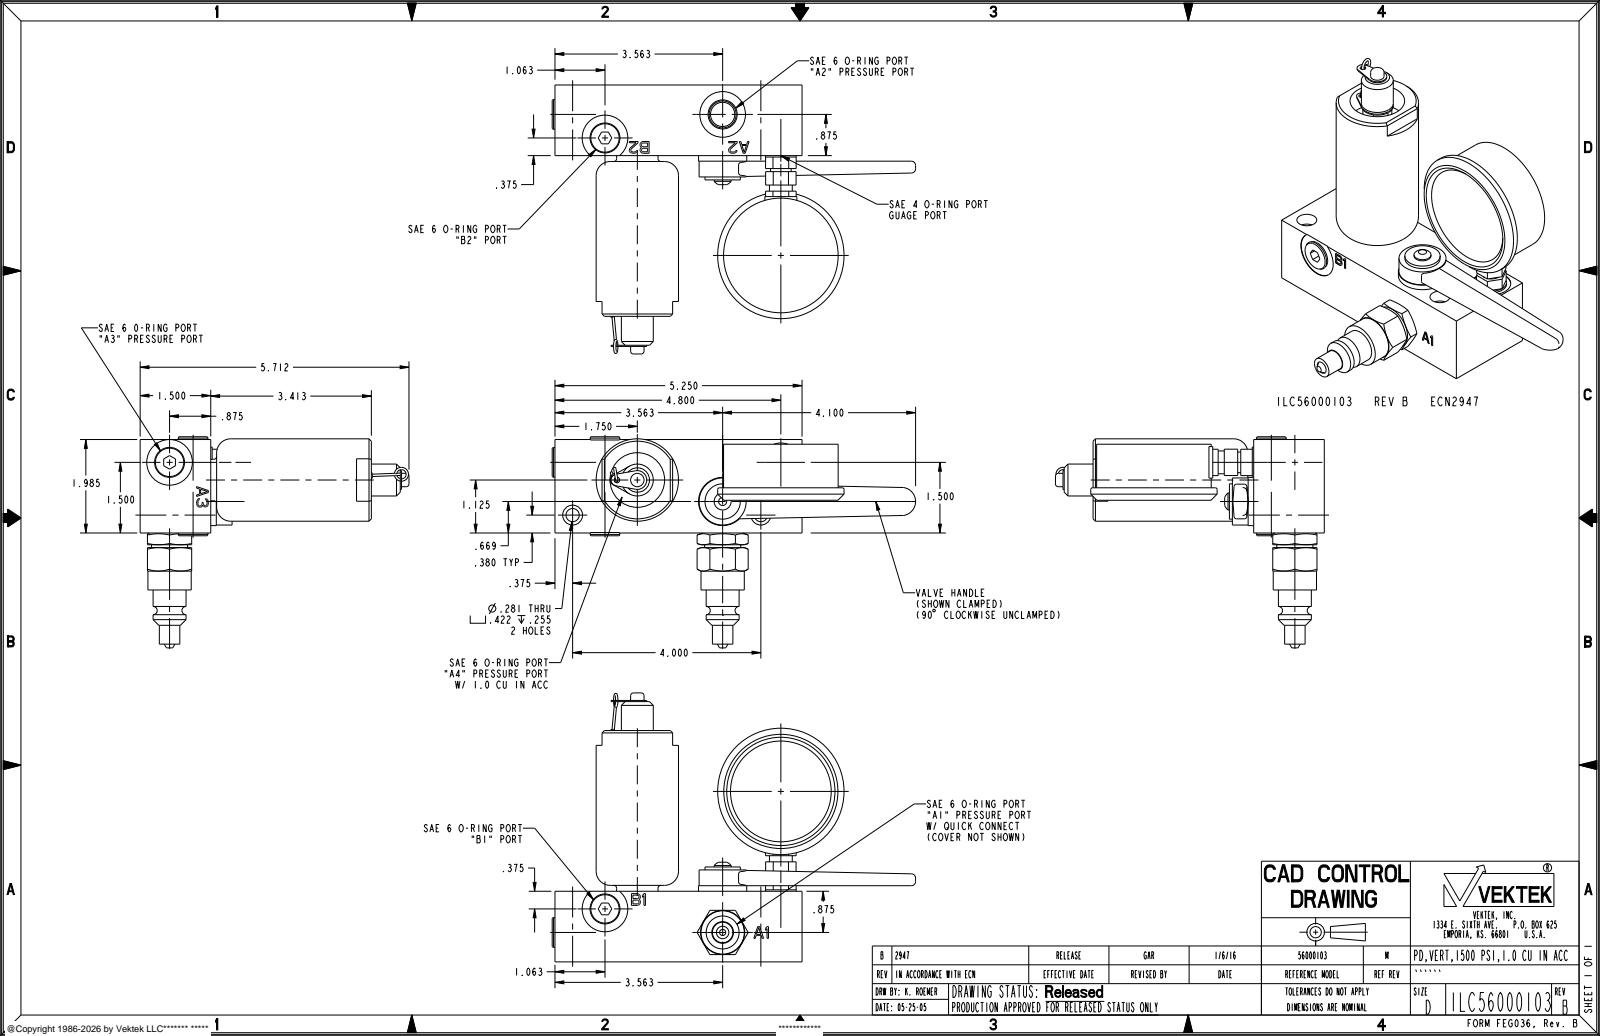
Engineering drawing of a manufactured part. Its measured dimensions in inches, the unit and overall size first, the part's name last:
Units: inches
Overall size (bounding box): 7.722 × 5.712 × 4.484
Round holes (diameter × count): ⌀0.515 ×4, ⌀0.97 ×3, ⌀0.118 ×2, ⌀0.281 ×2, ⌀0.422 ×2, ⌀0.12 ×1, ⌀0.265 ×1, ⌀0.392 ×1, ⌀0.442 ×1, ⌀0.498 ×1, ⌀0.825 ×1, ⌀1.16 ×1
Round bosses / shafts (diameter × count): ⌀0.563 ×4, ⌀0.51 ×2, ⌀2.685 ×1, ⌀2.435 ×1, ⌀1.75 ×1, ⌀1.024 ×1, ⌀1 ×1, ⌀0.92 ×1
Partial cylindrical surfaces — rounded edges, fillets, slot ends (radius × count): R0.09 ×2, R0.108 ×1, R0.125 ×1, R0.2 ×1, R0.3 ×1, R0.485 ×1
Main face-to-face distances: 1.5, 1.985, 0.1, 1.885, 1.21, 1.11, 0.775, 5.25, 0.51, 0.96
Hole centre spacings: 0.039, 0.433, 0.472, 1.171, 1.198, 1.201, 1.564, 2.55
Volume: 30.34 in³ · Surface area: 125.8 in²
Bodies: 5 solids, 618 faces (401 planar, 111 cylindrical, 106 other)
Part name (STEP PRODUCT): ILC56000103
STEP written by: PRO/ENGINEER BY PARAMETRIC TECHNOLOGY CORPORATION, 2013320 (AUTOMOTIVE_DESIGN)
